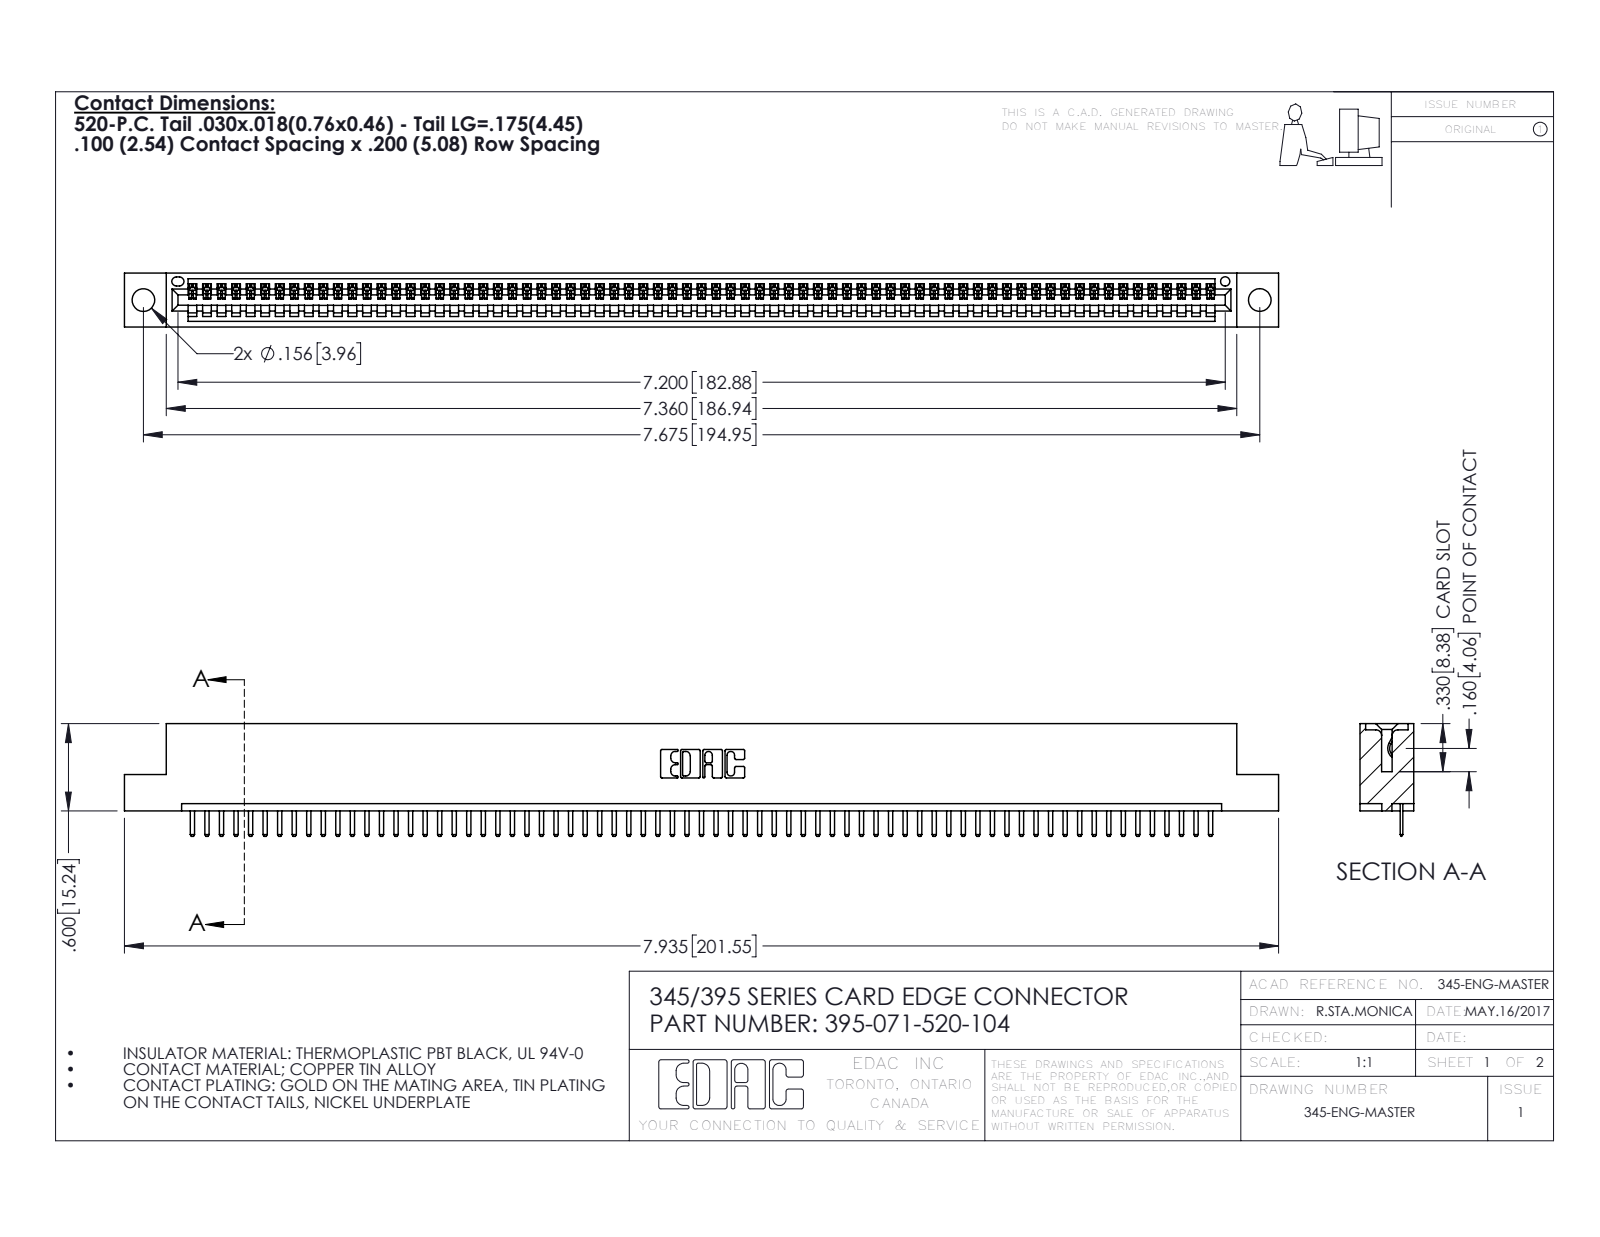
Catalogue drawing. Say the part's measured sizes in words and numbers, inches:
The part is named "345 Part_Flush Mounting Lugs - 0.156 Dia-TH; 345-292-001_345-293-120; 395-071-520-104". Its 3-D file was written by "SolidWorks 2016 (CONFIG_CONTROL_DESIGN)". It is 72 solids with 4528 faces: 3062 planar, 1466 cylindrical and 0 other. Overall it measures 7.935 by 0.775 by 0.37 inches. Its volume is 1.165 cubic inches and its surface area 38.6 square inches. Round holes: 2 of diameter 0.156, 1 of diameter 0.064. Partial cylindrical surfaces (rounded edges, fillets, slot ends): 144 of radius 0.01, 142 of radius 0.006, 22 of radius 0.01, 6 of radius 0.007, 6 of radius 0.031, 3 of radius 0.026, 2 of radius 0.031, 2 of radius 0.04. The main face-to-face distances are 0.298, 0.072, 0.37, 0.2, 0.098, 0.272, 0.025, 0.225, 0.072, 0.149. The hole center spacings are 0.27, 7.439, 7.675.
